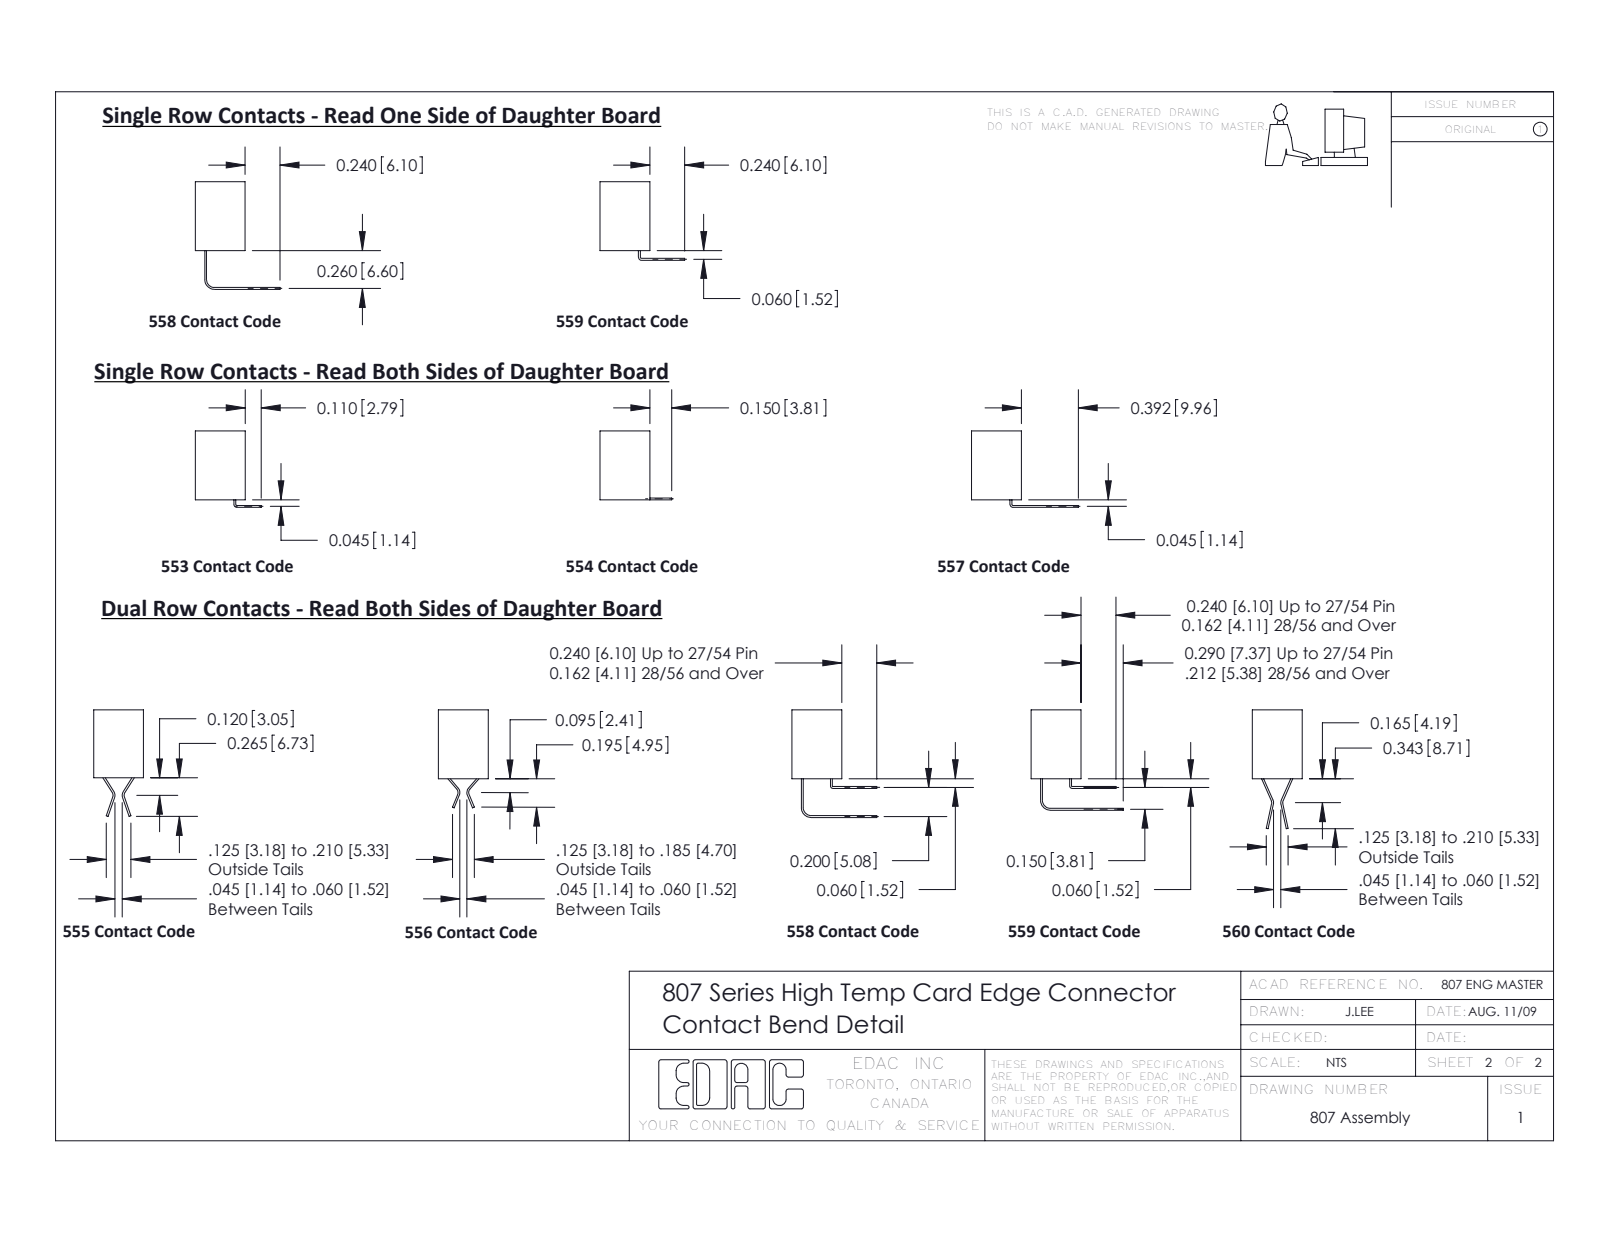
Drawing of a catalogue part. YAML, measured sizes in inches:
part_name: "307-290-001_527; 307 Part_.156 Dia Mounting Holes; 357-006-427-104"
step_written_by: "SolidWorks 2020 (CONFIG_CONTROL_DESIGN)"
units: inches
bodies: {solids: 7, faces: 475, planar: 306, cylindrical: 155, other: 14}
overall_size: [1.842, 0.831, 0.343]
volume: 0.176
surface_area: 5.847
round_holes:
  - {diameter: 0.156, count: 2}
partial_cylinders:
  - {radius: 0.02, count: 35}
  - {radius: 0.01, count: 22}
  - {radius: 0.007, count: 6}
  - {radius: 0.023, count: 6}
  - {radius: 0.031, count: 6}
  - {radius: 0.026, count: 3}
  - {radius: 0.046, count: 2}
  - {radius: 0.012, count: 1}
face_to_face_distances: [0.343, 0.278, 0.065, 0.156, 0.013, 0.265, 0.078, 0.246, 0.141, 0.202]
hole_center_spacings: [1.532]
